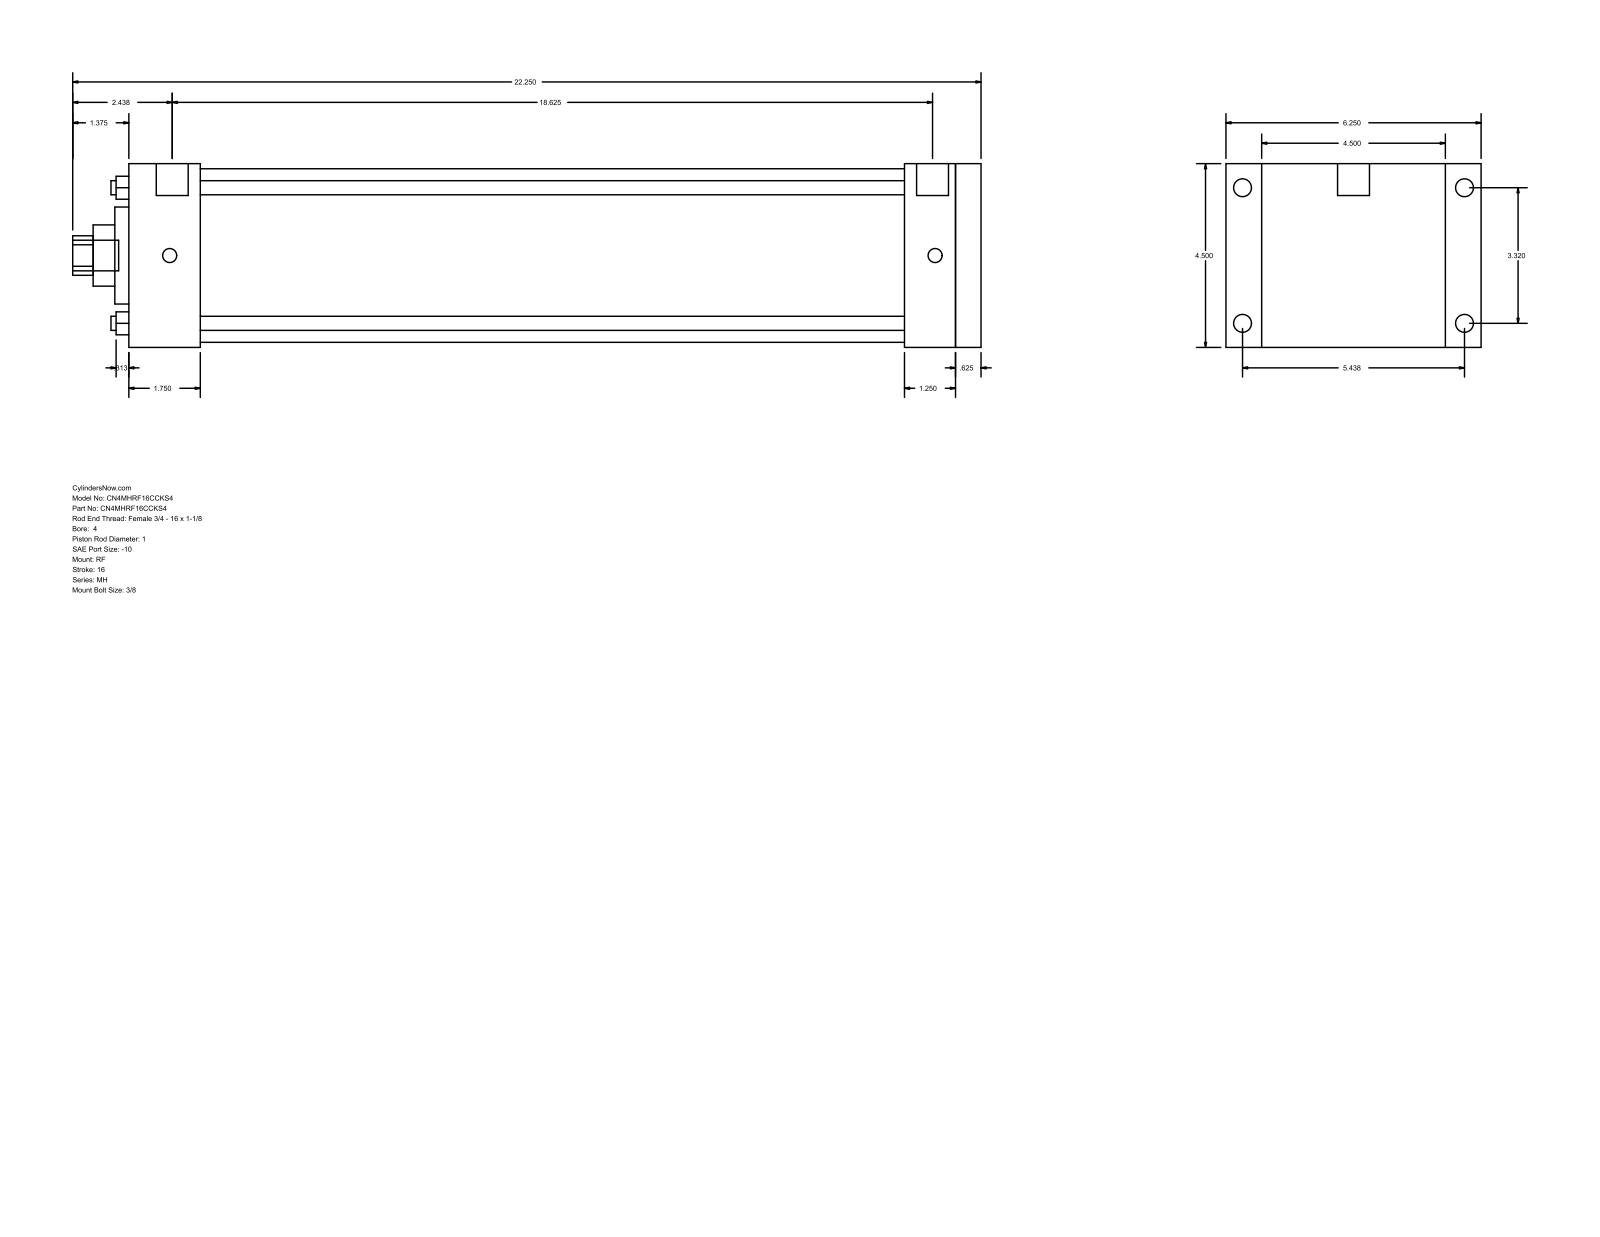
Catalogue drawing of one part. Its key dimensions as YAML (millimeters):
part_name: "MH_RF__0400_1"
step_written_by: "GSSL Pune (CONFIG_CONTROL_DESIGN)"
units: millimeters
bodies: {solids: 0, faces: 94, planar: 65, cylindrical: 29, other: 0}
overall_size: [565.15, 158.75, 114.3]
round_holes:
  - {diameter: 8.76, count: 4}
  - {diameter: 25.4, count: 1}
  - {diameter: 38.1, count: 1}
  - {diameter: 60.33, count: 1}
  - {diameter: 107.95, count: 1}
round_bosses_or_shafts:
  - {diameter: 11.13, count: 4}
  - {diameter: 8.73, count: 4}
  - {diameter: 19.84, count: 2}
  - {diameter: 19.05, count: 1}
partial_cylinders:
  - {radius: 12.29, count: 1}
face_to_face_distances: [114.3, 530.23, 514.35, 15.88, 47.63, 44.46, 469.89, 485.77, 482.6, 438.14]
hole_center_spacings: [59.62, 84.32, 119.25]
